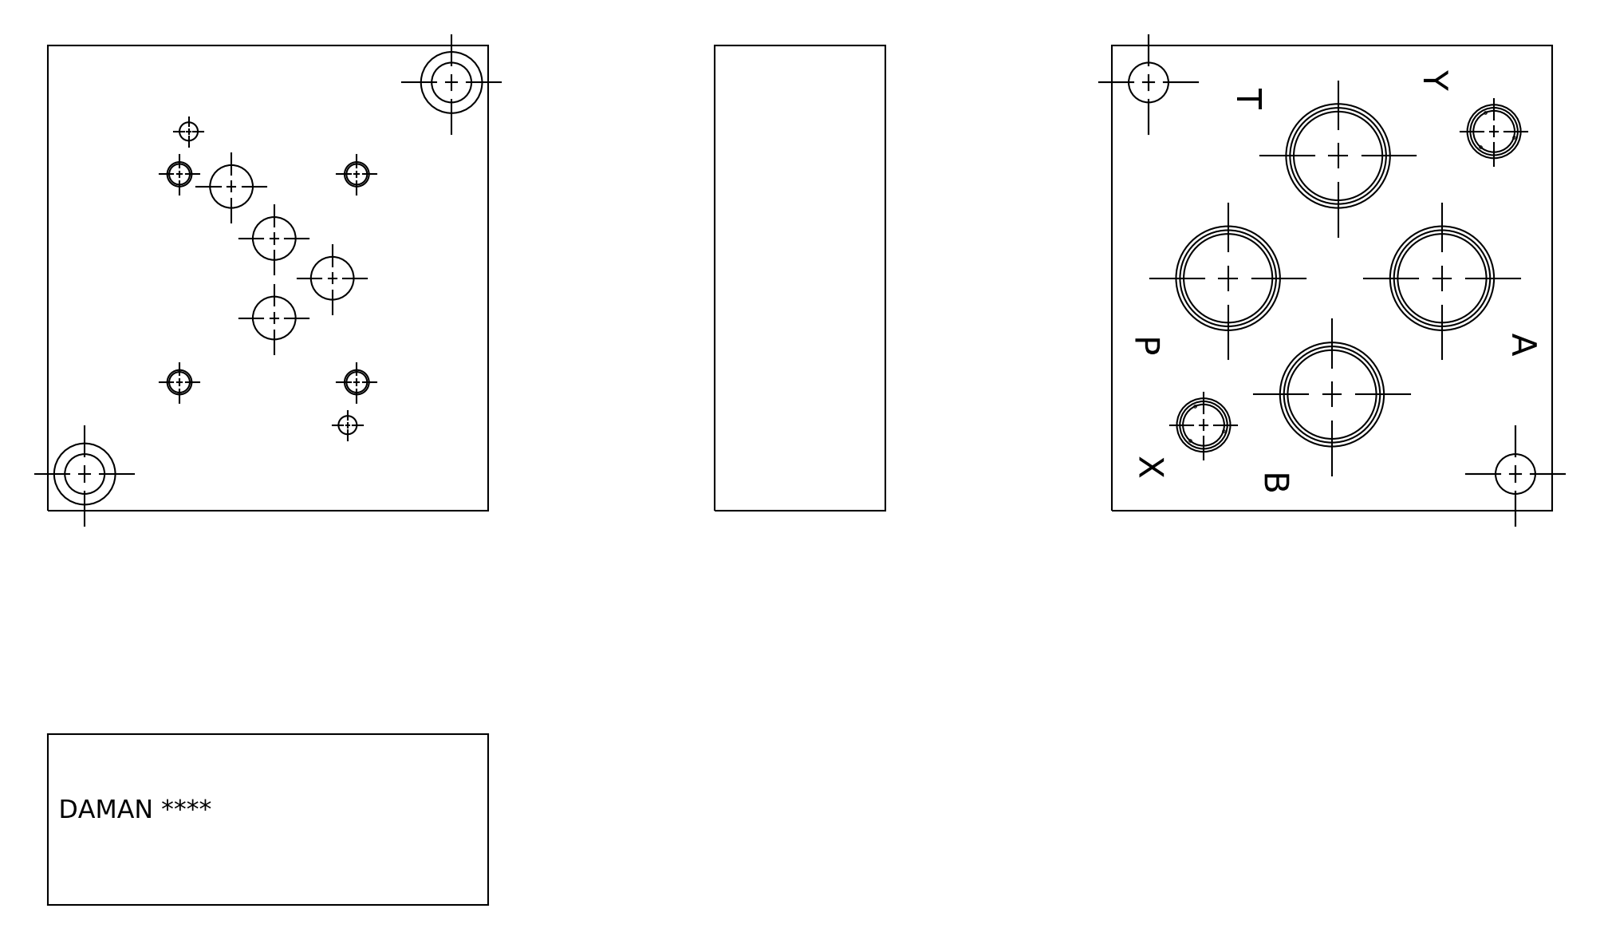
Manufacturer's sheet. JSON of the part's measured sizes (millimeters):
{"part_name": "Part__D05HSPB12P_3D", "step_written_by": "Autodesk Inventor 2020 (AUTOMOTIVE_DESIGN)", "units": "millimeters", "bodies": {"solids": 1, "faces": 494, "planar": 327, "cylindrical": 30, "other": 137}, "overall_size": [120.65, 114.3, 44.45], "volume_mm3": 553129, "surface_area_mm2": 60793, "round_holes": [[5.11, 4], [6.35, 4], [23.01, 4], [26.92, 4], [11.11, 3], [4.78, 2], [10.31, 2], [10.72, 2], [13.87, 2], [15.88, 2], [11.13, 1]], "face_to_face_distances": [44.45, 114.3, 120.65, 15.85, 28.6, 30.18, 14.33, 14.27, 120.61, 11.4], "hole_center_spacings": [31.91, 45.05, 48.02, 58.25, 78.38, 10.26, 11.21, 11.35]}
